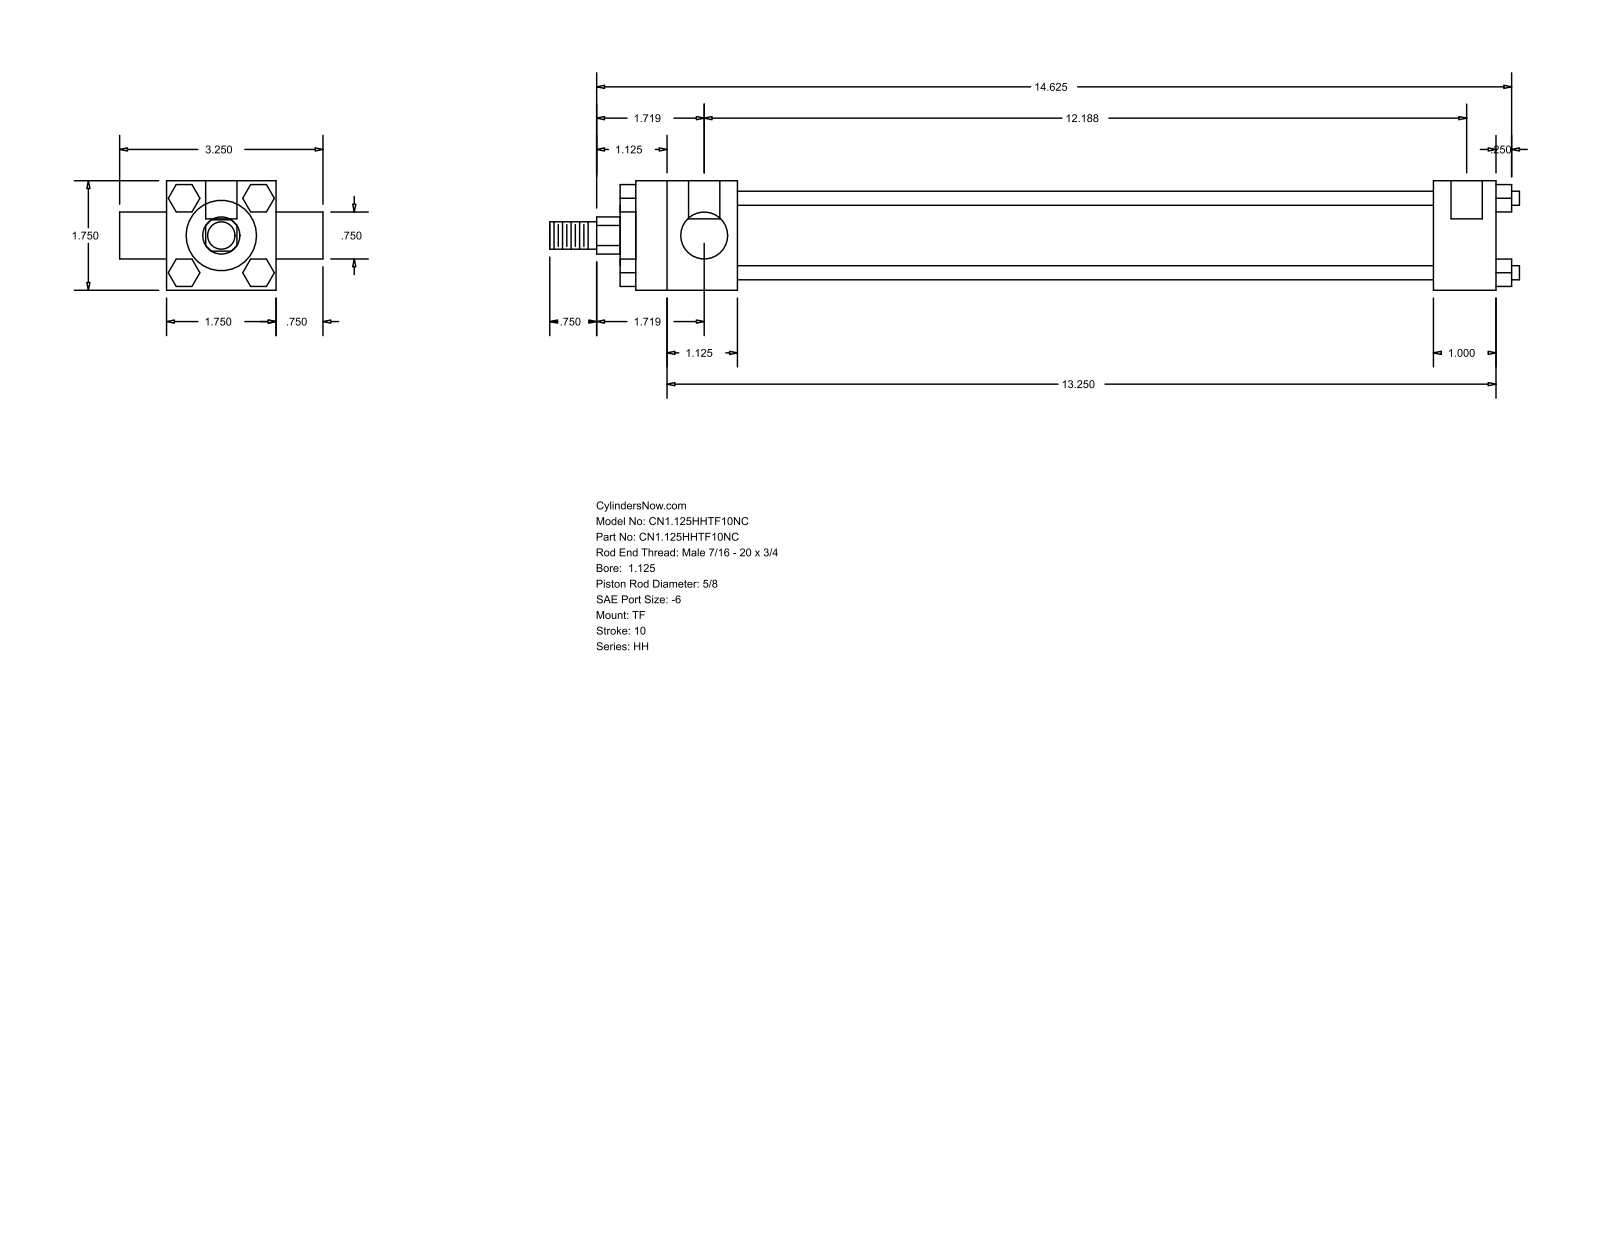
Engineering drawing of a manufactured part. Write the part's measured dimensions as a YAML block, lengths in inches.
part_name: "HH_TF__0112_0.625"
step_written_by: "GSSL Pune (CONFIG_CONTROL_DESIGN)"
units: inches
bodies: {solids: 0, faces: 120, planar: 92, cylindrical: 28, other: 0}
overall_size: [15.5, 3.25, 1.75]
round_holes:
  - {diameter: 0.219, count: 3}
  - {diameter: 0.5, count: 2}
round_bosses_or_shafts:
  - {diameter: 0.225, count: 4}
  - {diameter: 1.375, count: 1}
  - {diameter: 1.125, count: 1}
  - {diameter: 0.75, count: 1}
  - {diameter: 0.625, count: 1}
  - {diameter: 0.437, count: 1}
partial_cylinders:
  - {radius: 0.297, count: 1}
face_to_face_distances: [1.75, 0.437, 11.125, 12.125, 1, 1.625, 12.75, 13.75, 1.875, 0.25]
hole_center_spacings: [0.125, 12.063, 12.187]
